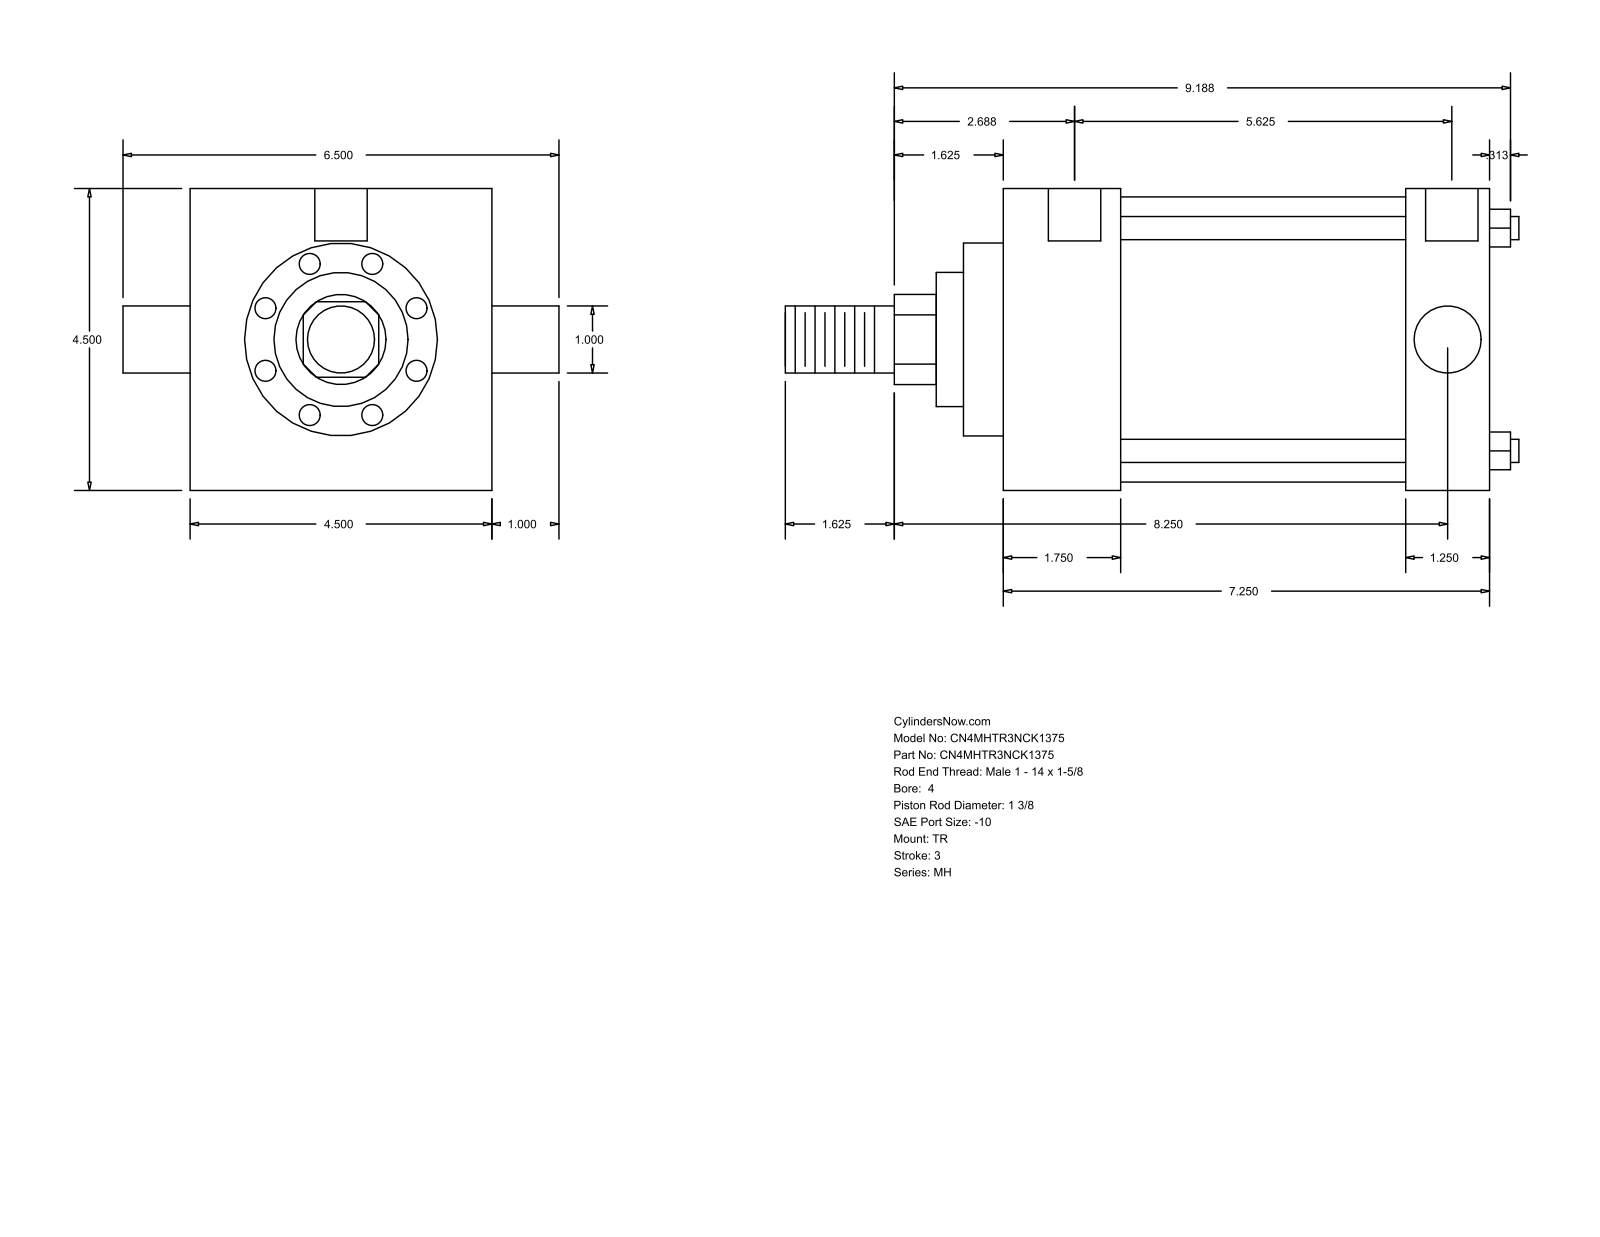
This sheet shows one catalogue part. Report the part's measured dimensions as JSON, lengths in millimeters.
{"part_name": "MH_TR__0400_1.375", "step_written_by": "GSSL Pune (CONFIG_CONTROL_DESIGN)", "units": "millimeters", "bodies": {"solids": 0, "faces": 86, "planar": 61, "cylindrical": 25, "other": 0}, "overall_size": [277.81, 165.1, 114.3], "round_holes": [[8.73, 3], [19.84, 2]], "round_bosses_or_shafts": [[8.76, 4], [25.4, 2], [107.95, 1], [73.03, 1], [50.8, 1], [34.92, 1]], "partial_cylinders_radius": [[17.06, 1]], "face_to_face_distances": [114.3, 184.16, 44.45, 139.71, 152.41, 107.96, 31.75, 15.08, 59.53, 167.49], "hole_center_spacings": [1.58, 1.59, 142.88, 144.46, 144.47, 146.05]}
